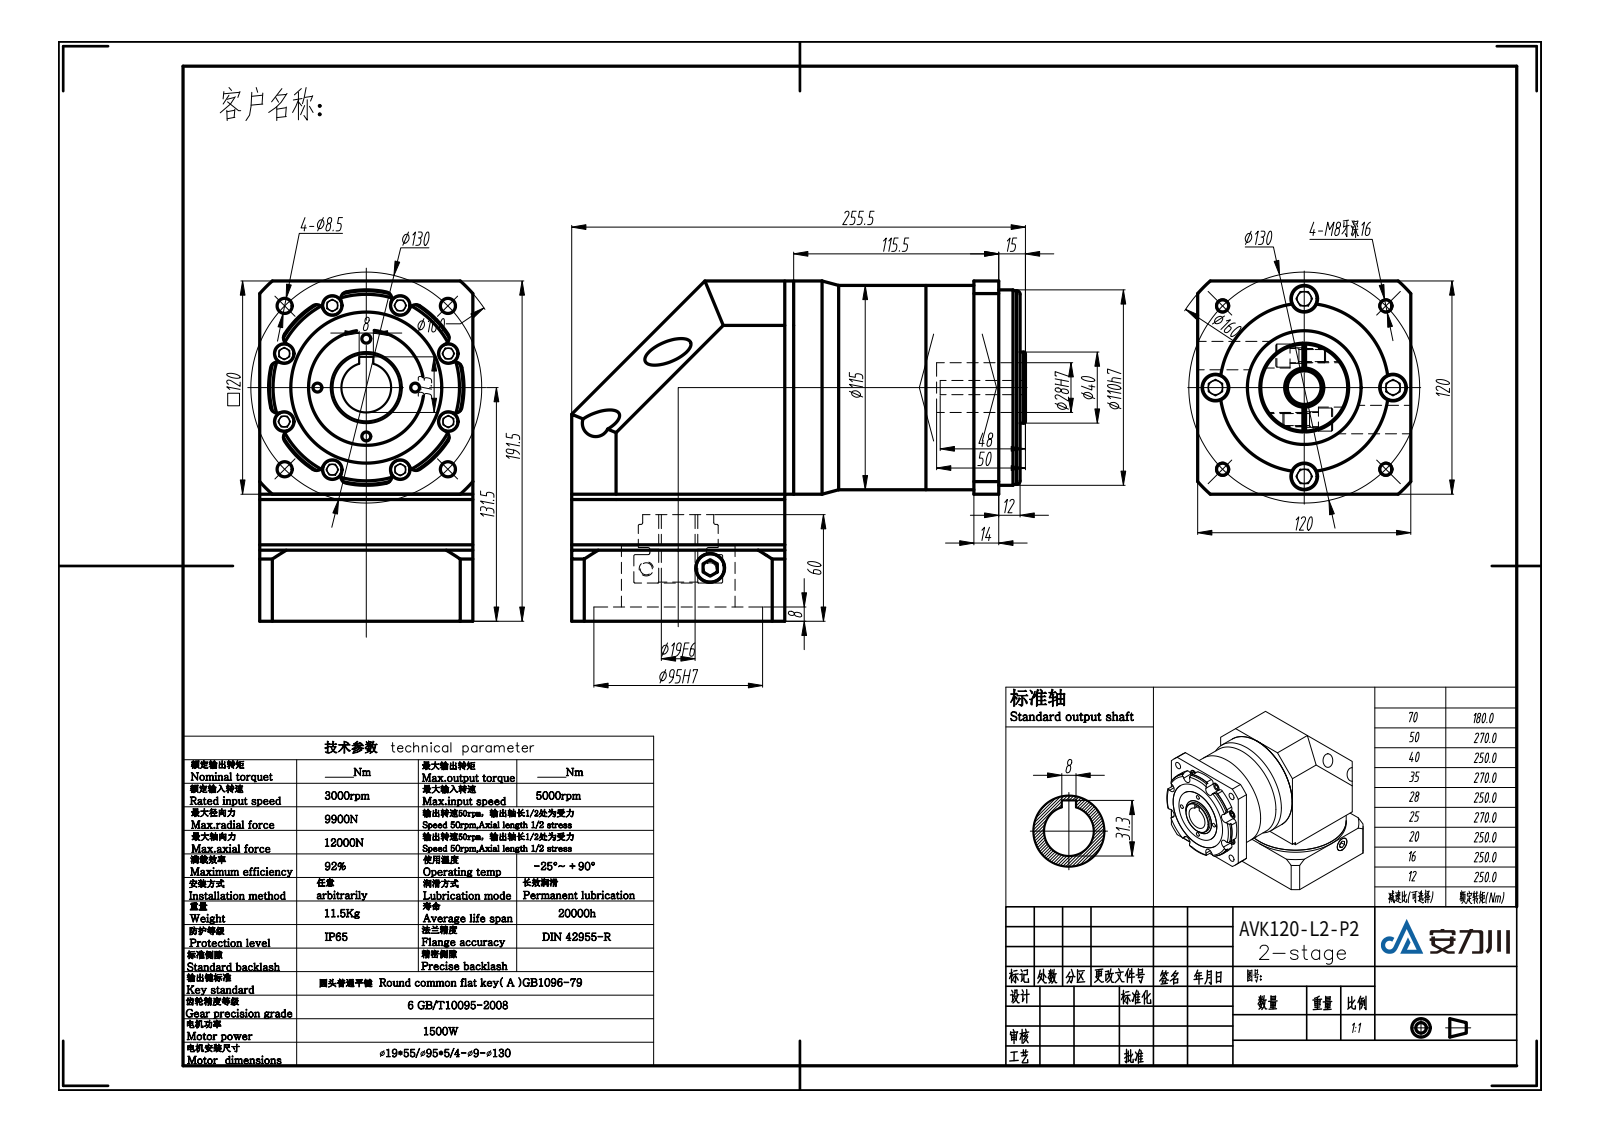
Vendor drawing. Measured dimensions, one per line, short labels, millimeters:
name: VGZK115双级模型（19-55 95-5 4-9-130）
written by: SolidWorks 2016 (AUTOMOTIVE_DESIGN)
unit: mm
bodies: 23 solids, 506 faces (279 planar, 202 cylindrical, 25 other)
size: 255.5 × 191.5 × 120
volume: 3 381 000 mm³; area: 352 507 mm²
holes: 10× ⌀15, 8× ⌀11, 4× ⌀5, 4× ⌀6.8, 4× ⌀8.5, 2× ⌀16, 1× ⌀19, 1× ⌀20, 1× ⌀22, 1× ⌀28, 1× ⌀45.2, 1× ⌀70
bosses: 10× ⌀13, 8× ⌀9.5, 2× ⌀120, 2× ⌀15.6, 1× ⌀115, 1× ⌀65, 1× ⌀50, 1× ⌀45
rounds: 16× R4, 2× R80, 1× R54.5, 1× R55
face distances: 5, 120, 25.5, 49.17, 74.5, 79.5, 25.33, 30.33, 199.5, 43
hole spacings: 39.29, 94.69, 26.74, 26.83, 46.14, 46.94, 49.53, 49.99
